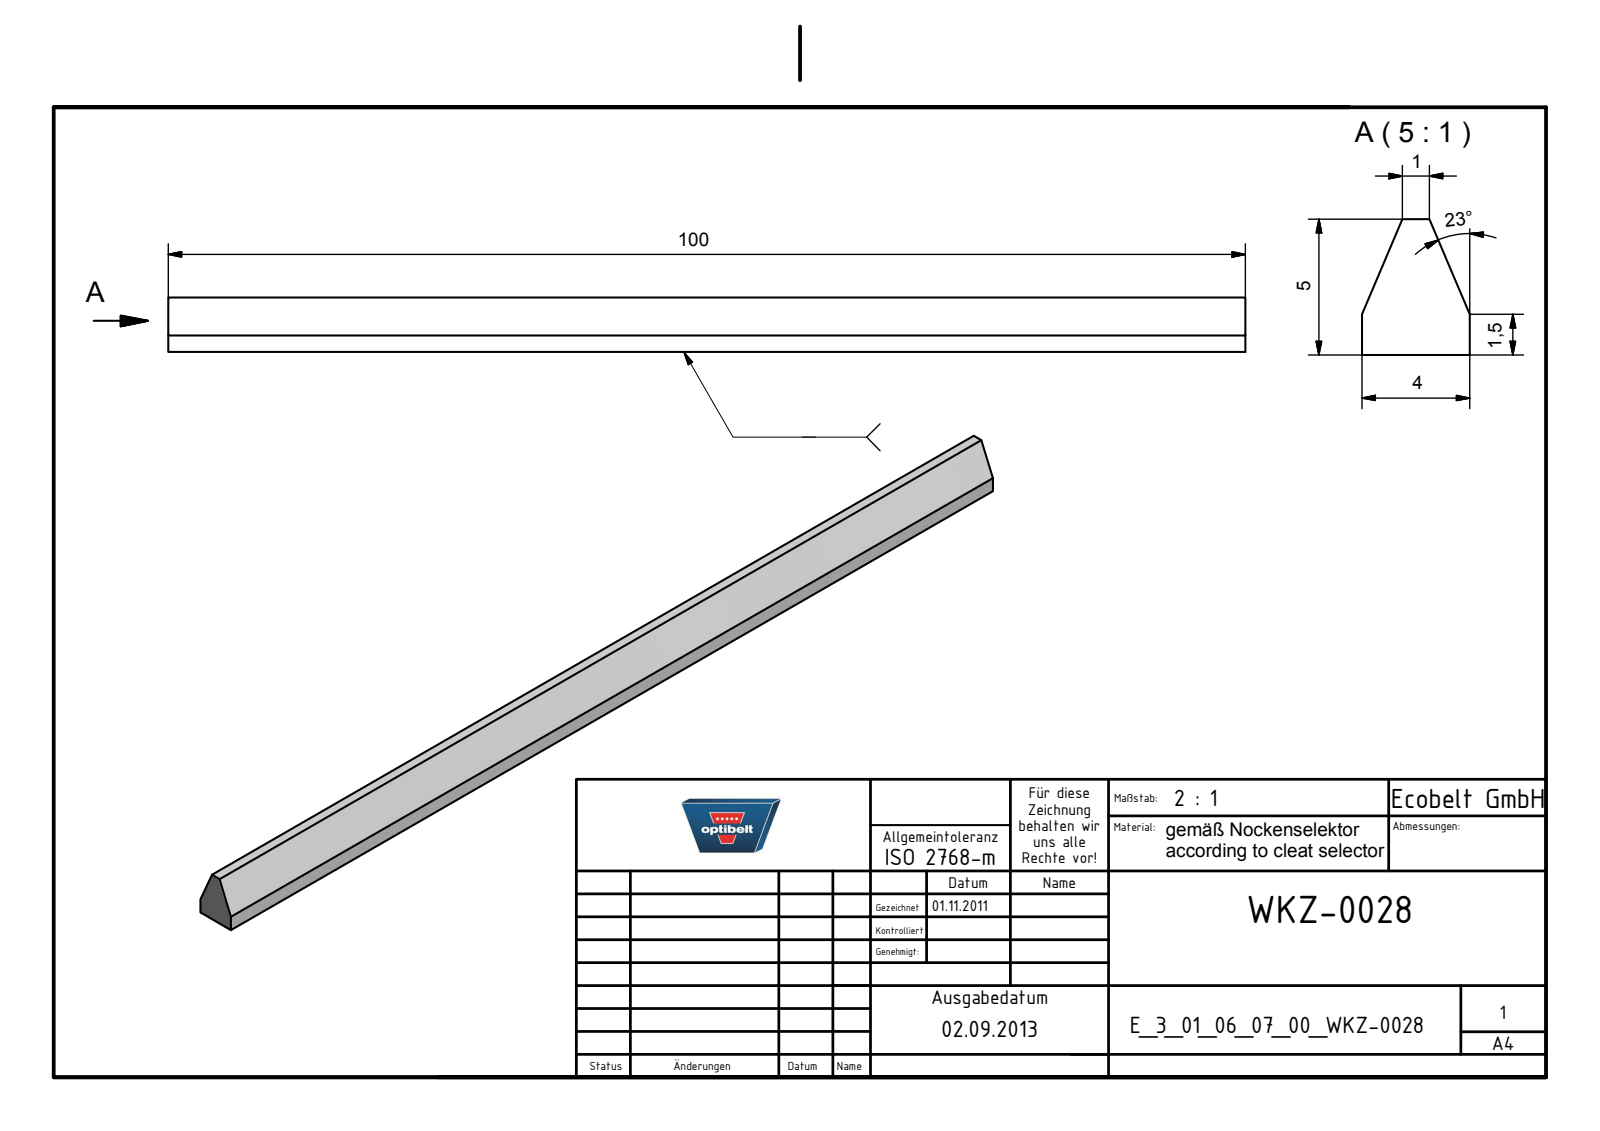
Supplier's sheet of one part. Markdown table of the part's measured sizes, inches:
| quantity | value |
| --- | --- |
| part name | E_3_01_06_07_00_WKZ-0028 |
| STEP written by | Autodesk Inventor 2021 (AUTOMOTIVE_DESIGN) |
| units | inches |
| bodies | 1 solid, 8 faces (8 planar, 0 cylindrical, 0 other) |
| overall size | 3.937 × 0.198 × 0.157 |
| volume | 0.09 in³ |
| surface area | 2.475 in² |
| main face-to-face distances | 0.157, 0.198, 3.937 |
